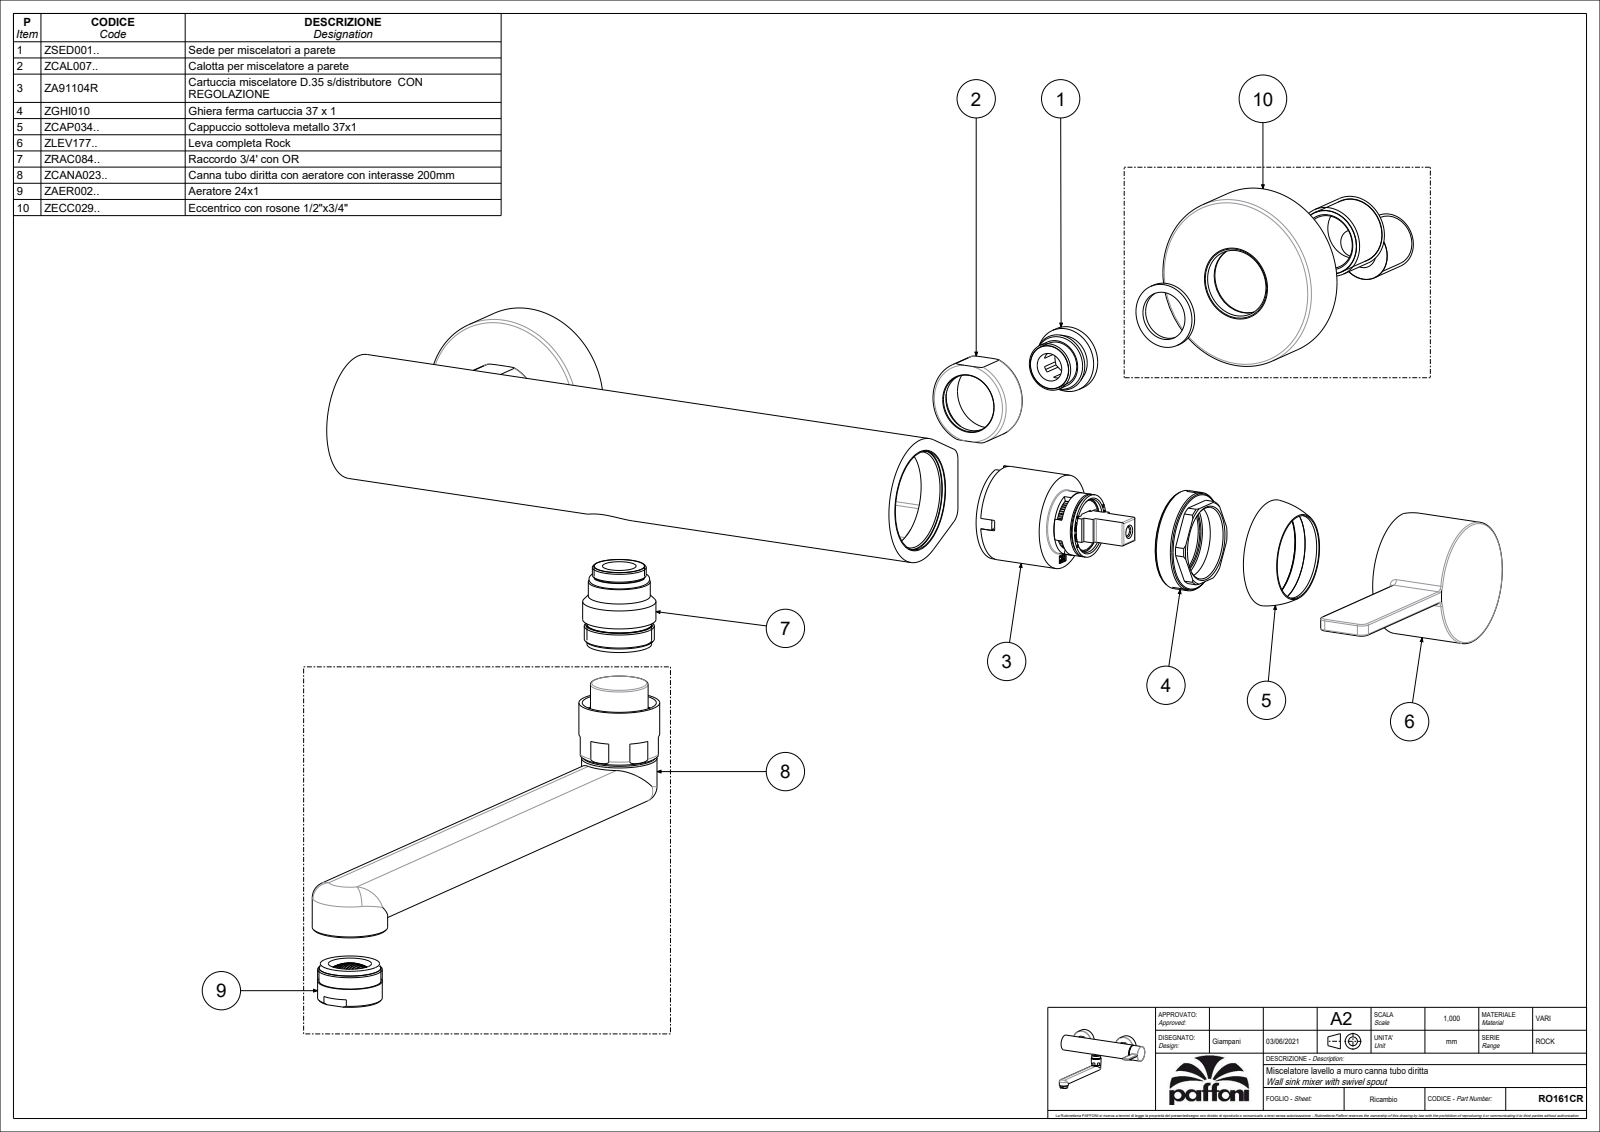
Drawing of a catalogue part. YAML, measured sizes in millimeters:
part_name: "RO161CR"
step_written_by: "CREO PARAMETRIC BY PTC INC, 2020044 (CONFIG_CONTROL_DESIGN)"
units: millimeters
bodies: {solids: 0, faces: 146, planar: 49, cylindrical: 45, other: 52}
overall_size: [277, 273.1, 114.2]
round_bosses_or_shafts:
  - {diameter: 63.5, count: 2}
  - {diameter: 28, count: 2}
  - {diameter: 24, count: 2}
  - {diameter: 45.5, count: 1}
  - {diameter: 30, count: 1}
  - {diameter: 27.2, count: 1}
  - {diameter: 23, count: 1}
  - {diameter: 7.6, count: 1}
partial_cylinders:
  - {radius: 0.5, count: 6}
  - {radius: 2, count: 2}
  - {radius: 3, count: 2}
  - {radius: 5, count: 2}
  - {radius: 8, count: 2}
  - {radius: 15.6, count: 2}
  - {radius: 18.5, count: 2}
  - {radius: 23.25, count: 1}
face_to_face_distances: [20, 35, 15, 16, 241, 35.5, 15.5, 0.5, 33.7, 13.7]
